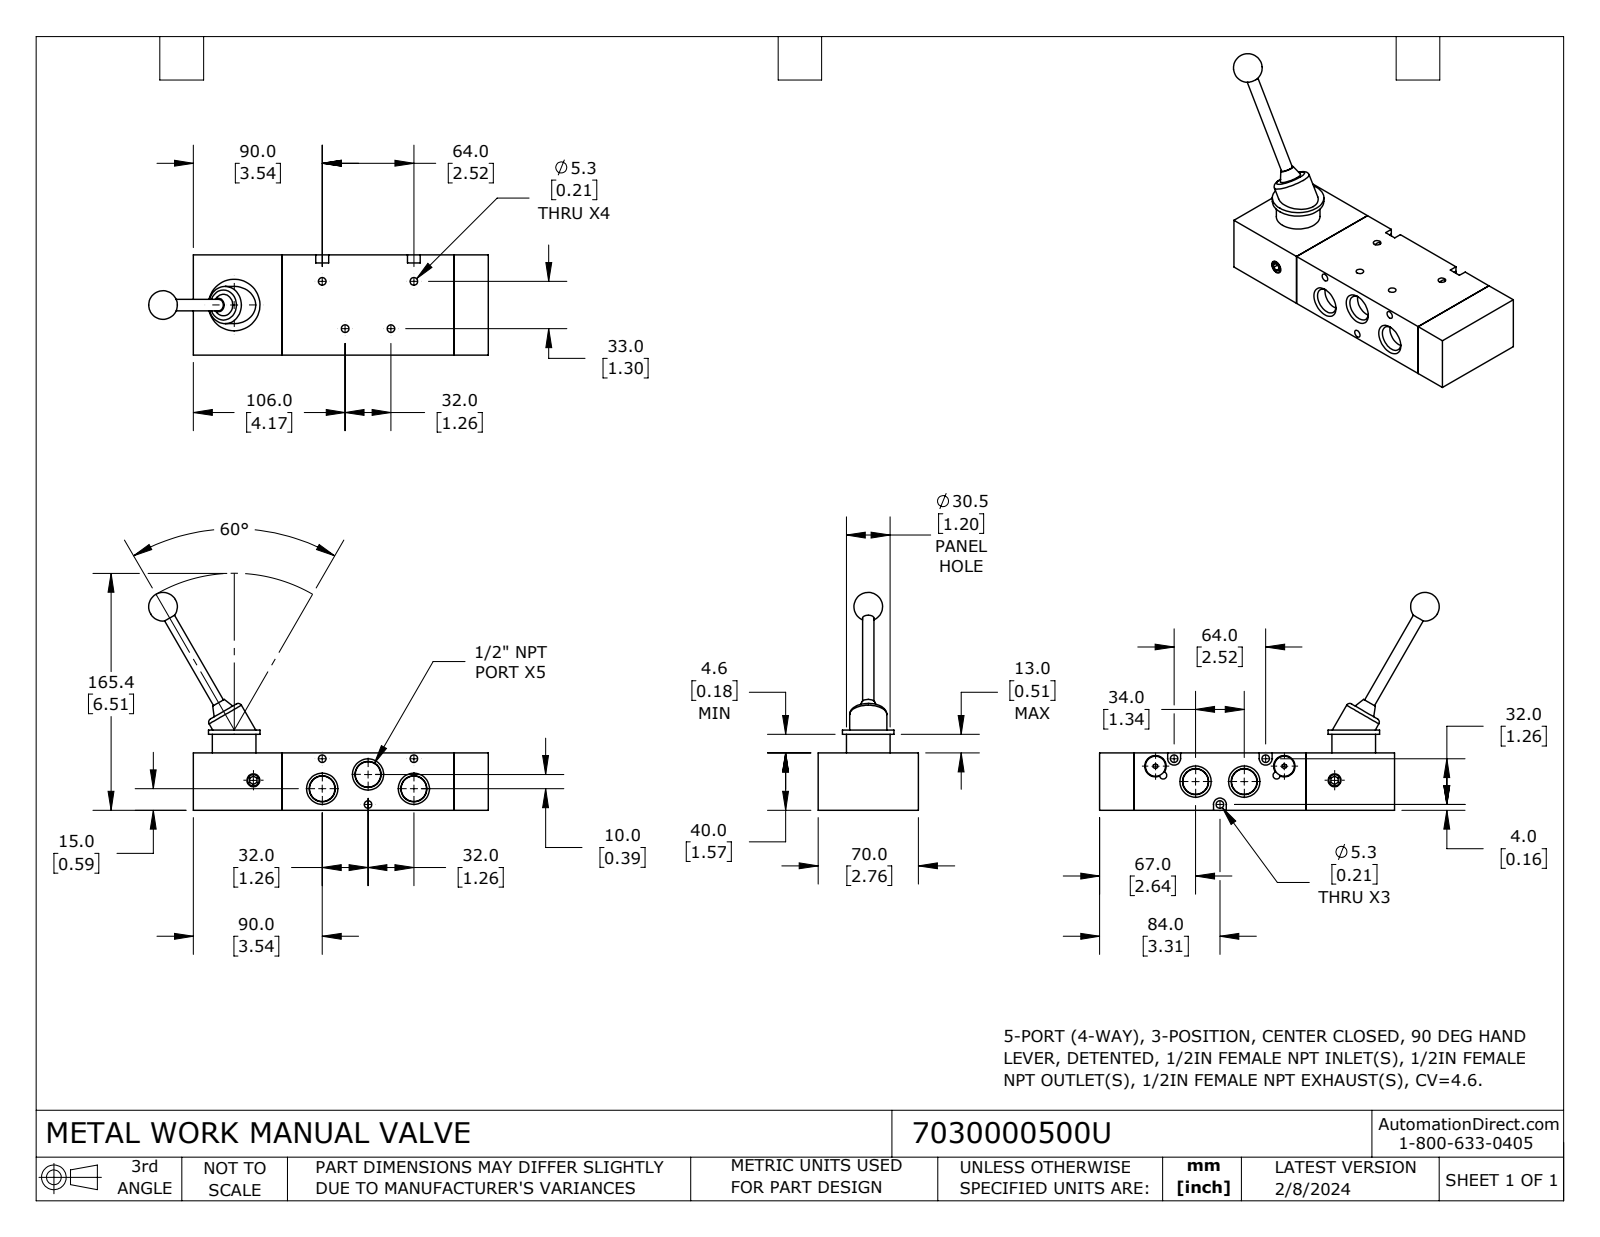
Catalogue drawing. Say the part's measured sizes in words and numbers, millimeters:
The part is named "7030000500U". Its 3-D file was written by "SolidWorks 2023 (CONFIG_CONTROL_DESIGN)". It is 3 solids with 155 faces: 72 planar, 57 cylindrical and 26 other. Overall it measures 237.2 by 152.1 by 70 millimeters. Its volume is 584 200 cubic millimeters and its surface area 77 940 square millimeters. Round holes: 7 of diameter 5.3, 2 of diameter 14.9, 1 of diameter 9. Round bosses or shafts: 2 of diameter 14, 1 of diameter 36, 1 of diameter 30.5, 1 of diameter 26, 1 of diameter 8, 1 of diameter 8. Partial cylindrical surfaces (rounded edges, fillets, slot ends): 3 of radius 4.5, 2 of radius 2.5. The main face-to-face distances are 40, 70, 120, 24, 144, 206, 182, 62, 9, 61. The hole center spacings are 14, 36.7, 45.2, 52.3, 58.2, 64, 77.2, 32.
